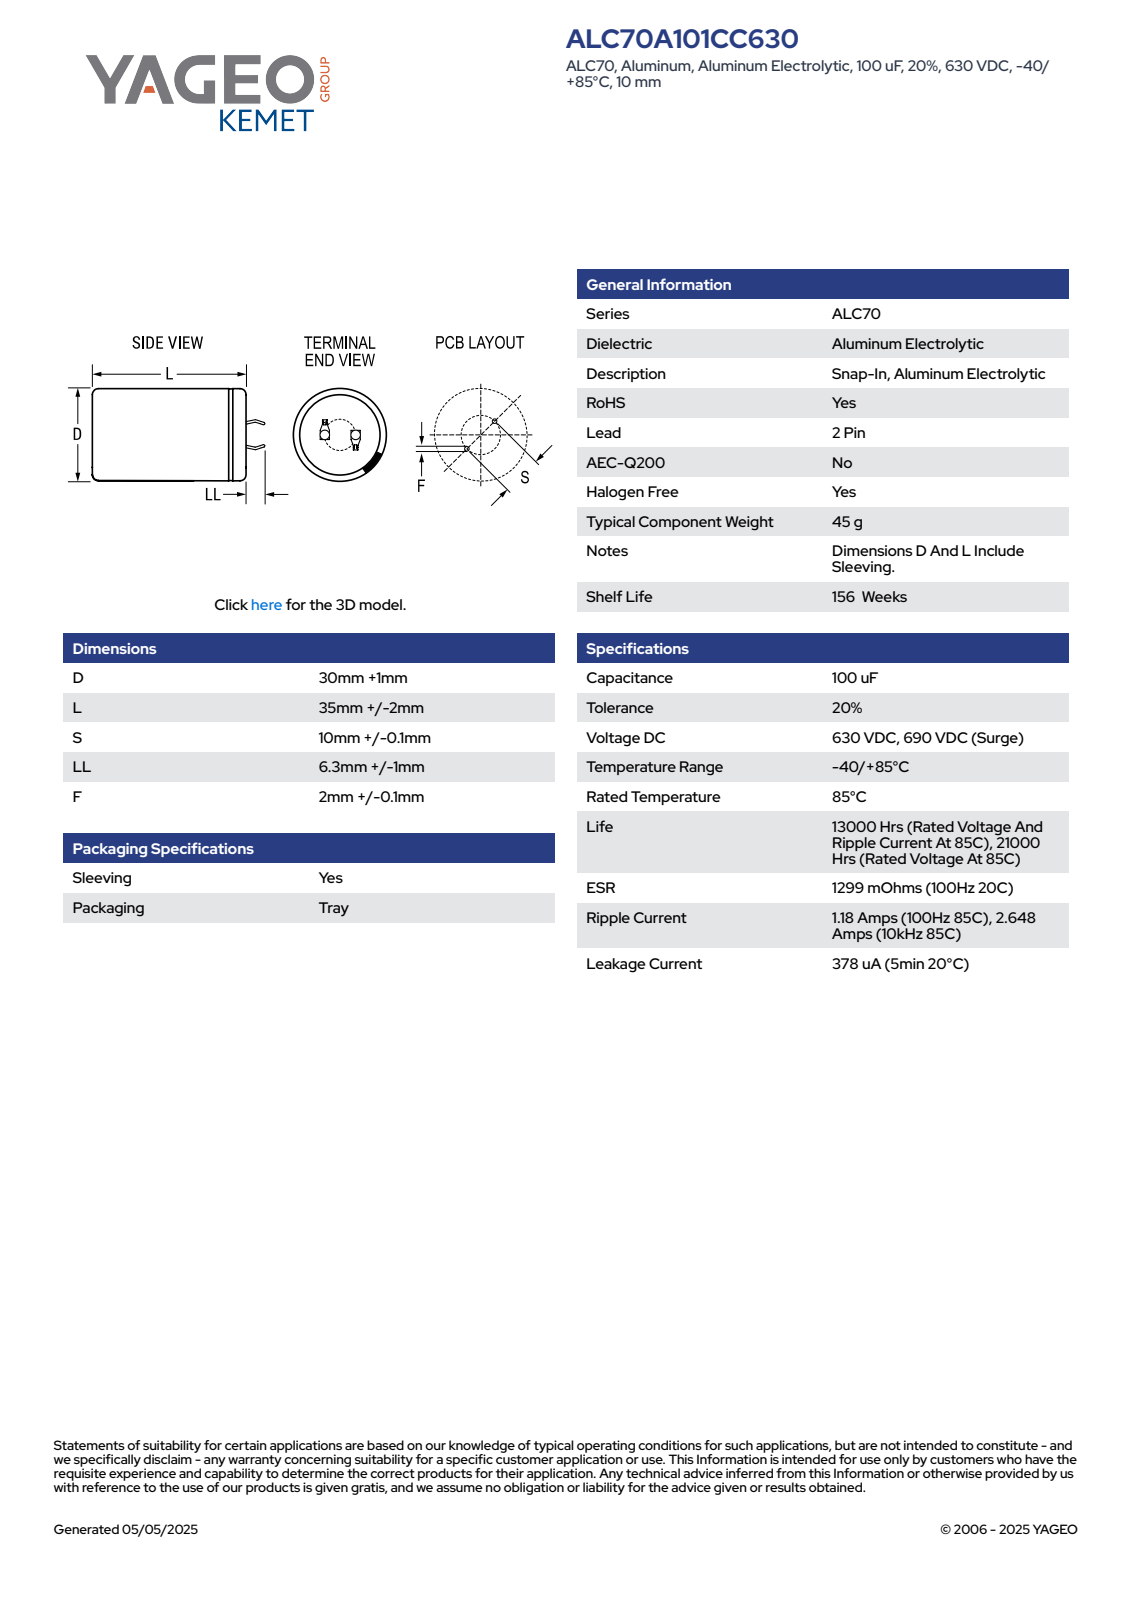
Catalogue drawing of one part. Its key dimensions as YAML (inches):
part_name: "CARS_K2P_30X35_D31L37S10LL7.3F2.1"
step_written_by: "SolidWorks 2014 (AUTOMOTIVE_DESIGN)"
units: inches
bodies: {solids: 1, faces: 100, planar: 52, cylindrical: 9, other: 39}
overall_size: [1.744, 1.22, 1.22]
volume: 1.684
surface_area: 7.941
round_holes:
  - {diameter: 1.08, count: 1}
round_bosses_or_shafts:
  - {diameter: 1.22, count: 1}
partial_cylinders:
  - {radius: 0.61, count: 1}
face_to_face_distances: [1.456, 0.024, 1.476, 0.02, 0.279, 0.301, 0.03, 0.053, 0.302, 0.255]
